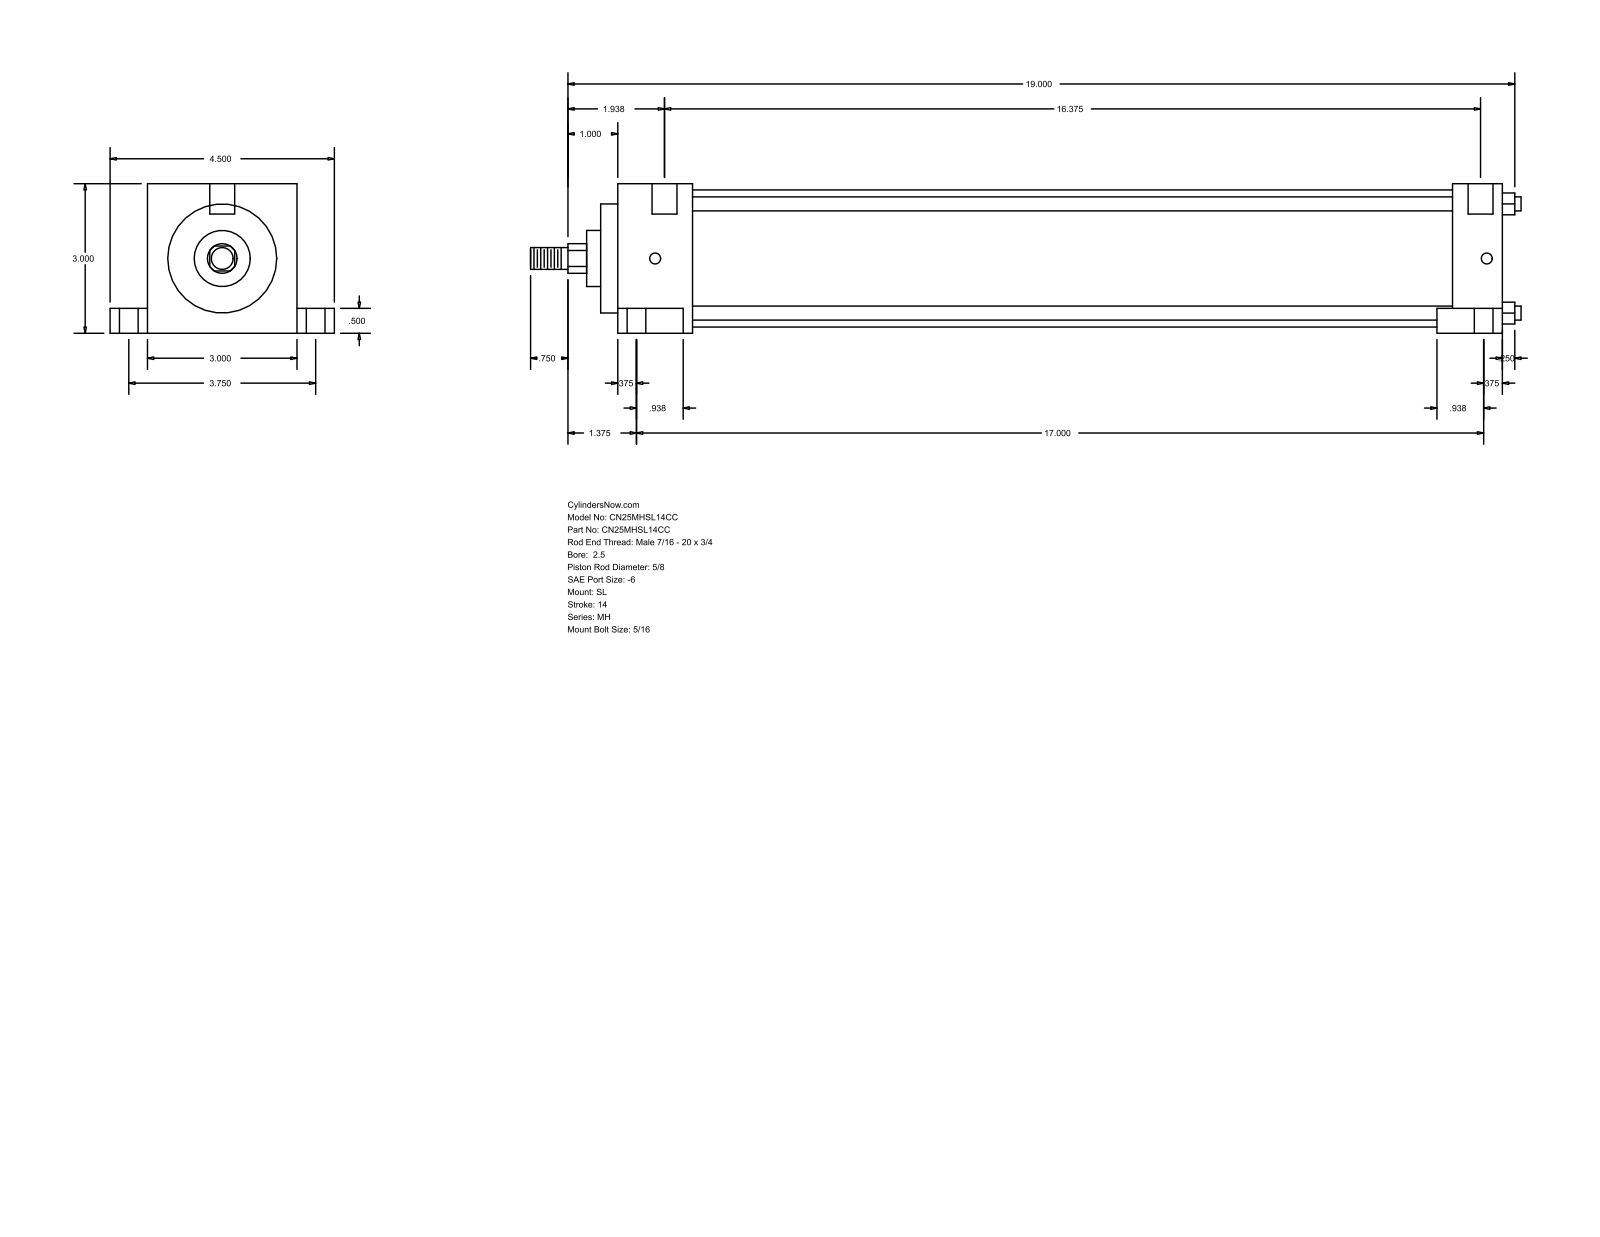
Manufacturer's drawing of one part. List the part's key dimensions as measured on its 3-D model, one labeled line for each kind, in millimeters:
Part name (STEP PRODUCT): MH_SL__0250_0.625
STEP written by: GSSL Pune (CONFIG_CONTROL_DESIGN)
Units: millimetres
Bodies: 0 solids, 86 faces (61 planar, 25 cylindrical, 0 other)
Overall size (bounding box): 504.82 × 114.3 × 76.2
Round holes (diameter × count): ⌀5.56 ×2, ⌀9.53 ×2, ⌀15.88 ×2, ⌀12.7 ×1
Round bosses / shafts (diameter × count): ⌀7.14 ×4, ⌀69.85 ×1, ⌀55.55 ×1, ⌀28.57 ×1, ⌀15.88 ×1, ⌀11.11 ×1
Partial cylindrical surfaces — rounded edges, fillets, slot ends (radius × count): R7.54 ×1
Main face-to-face distances: 76.2, 25.4, 434.18, 459.58, 63.5, 12.7, 19.05, 95.25, 31.75, 426.24
Hole centre spacings: 47.65, 3.17, 95.24
